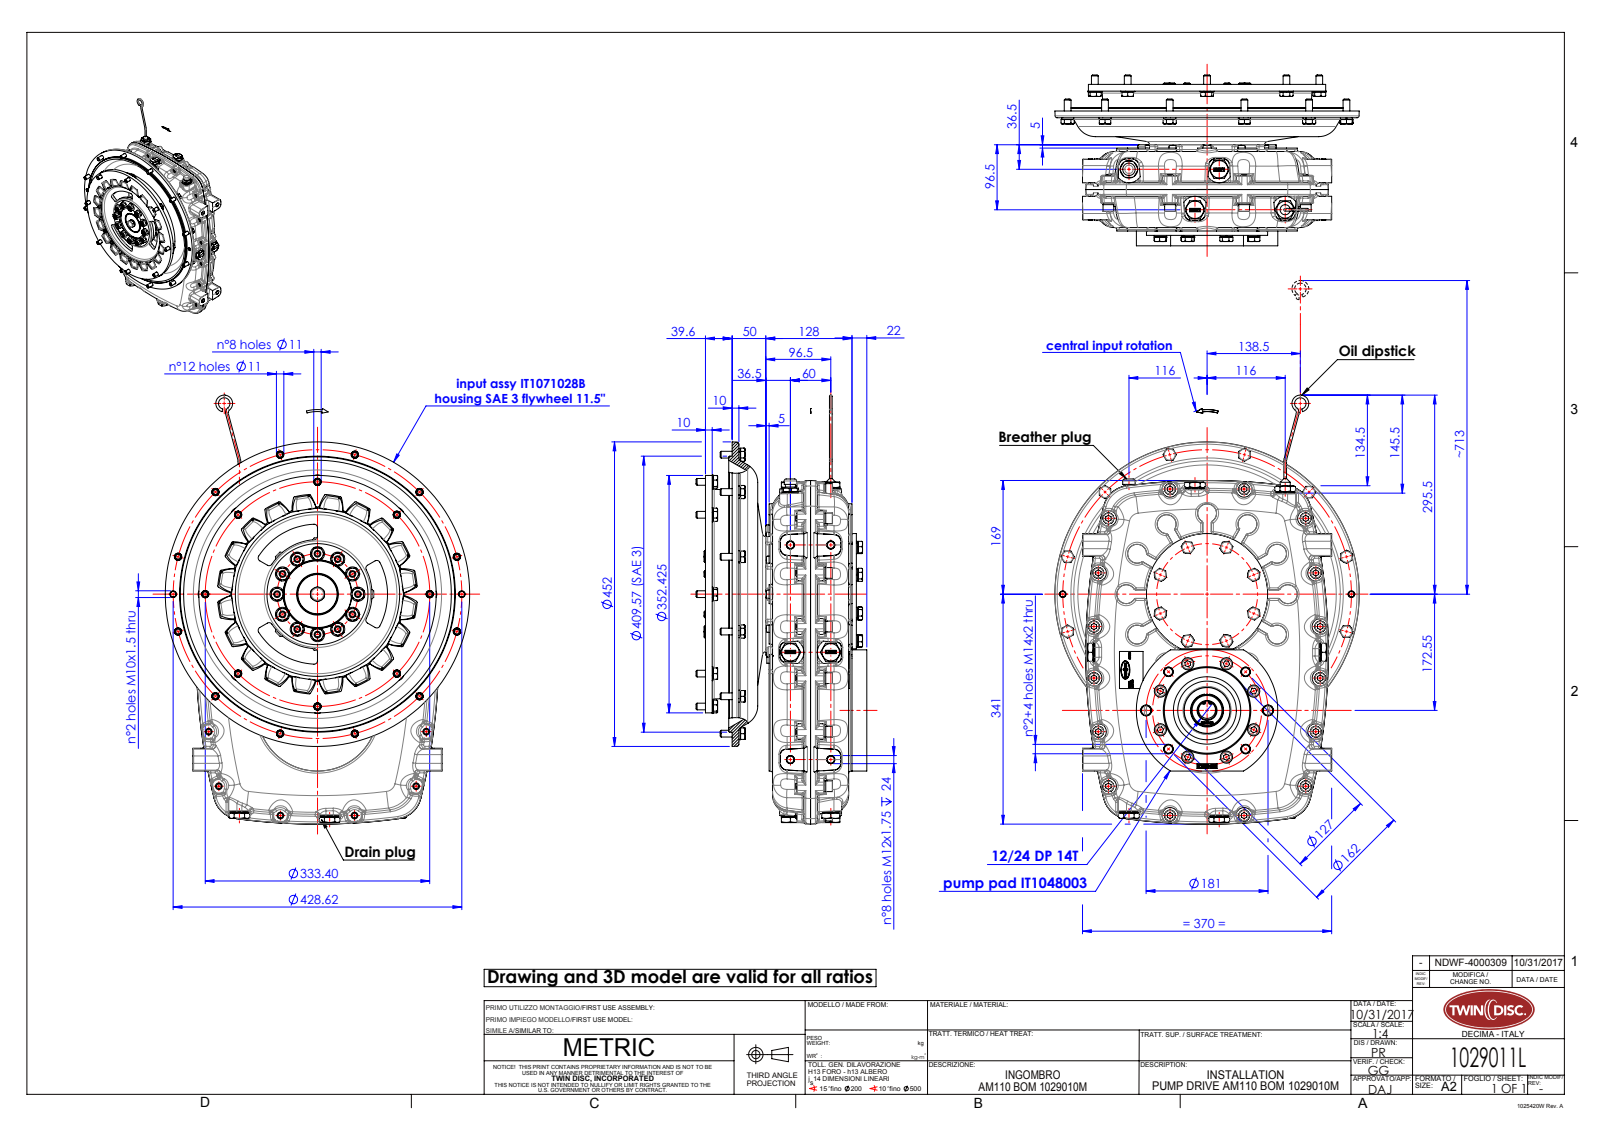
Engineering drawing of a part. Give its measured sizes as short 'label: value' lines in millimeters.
name: ITam110-001_rev01-installation; ITam110-002_rev00-installation; IT1048003_rev00-installation; IT0001009_rev00-installation (+4 more)
written by: SolidWorks 2015 (AUTOMOTIVE_DESIGN)
unit: mm
bodies: 77 solids, 8117 faces (3111 planar, 1569 cylindrical, 3437 other)
size: 636.78 × 452.05 × 253.6
volume: 5 416 000 mm³; area: 2 505 000 mm²
holes: 60× ⌀10.2, 44× ⌀11, 41× ⌀8.5, 28× ⌀10.5, 19× ⌀12, 9× ⌀18.63, 9× ⌀21, 8× ⌀18, 6× ⌀14, 2× ⌀2, 2× ⌀16, 2× ⌀70
bosses: 74× ⌀10, 48× ⌀16.2, 28× ⌀18.1, 24× ⌀16, 20× ⌀21, 16× ⌀16.1, 9× ⌀27, 8× ⌀25.95
rounds: 166× R3, 80× R1, 80× R4, 40× R2.5, 40× R42.91, 24× R12, 20× R10, 12× R5
face distances: 61.5, 5, 56.5, 30, 118, 148, 86.5, 10, 20, 39.6
hole spacings: 120, 207.84, 231.82, 51.37, 123.96, 157.1, 169.7, 193.41
